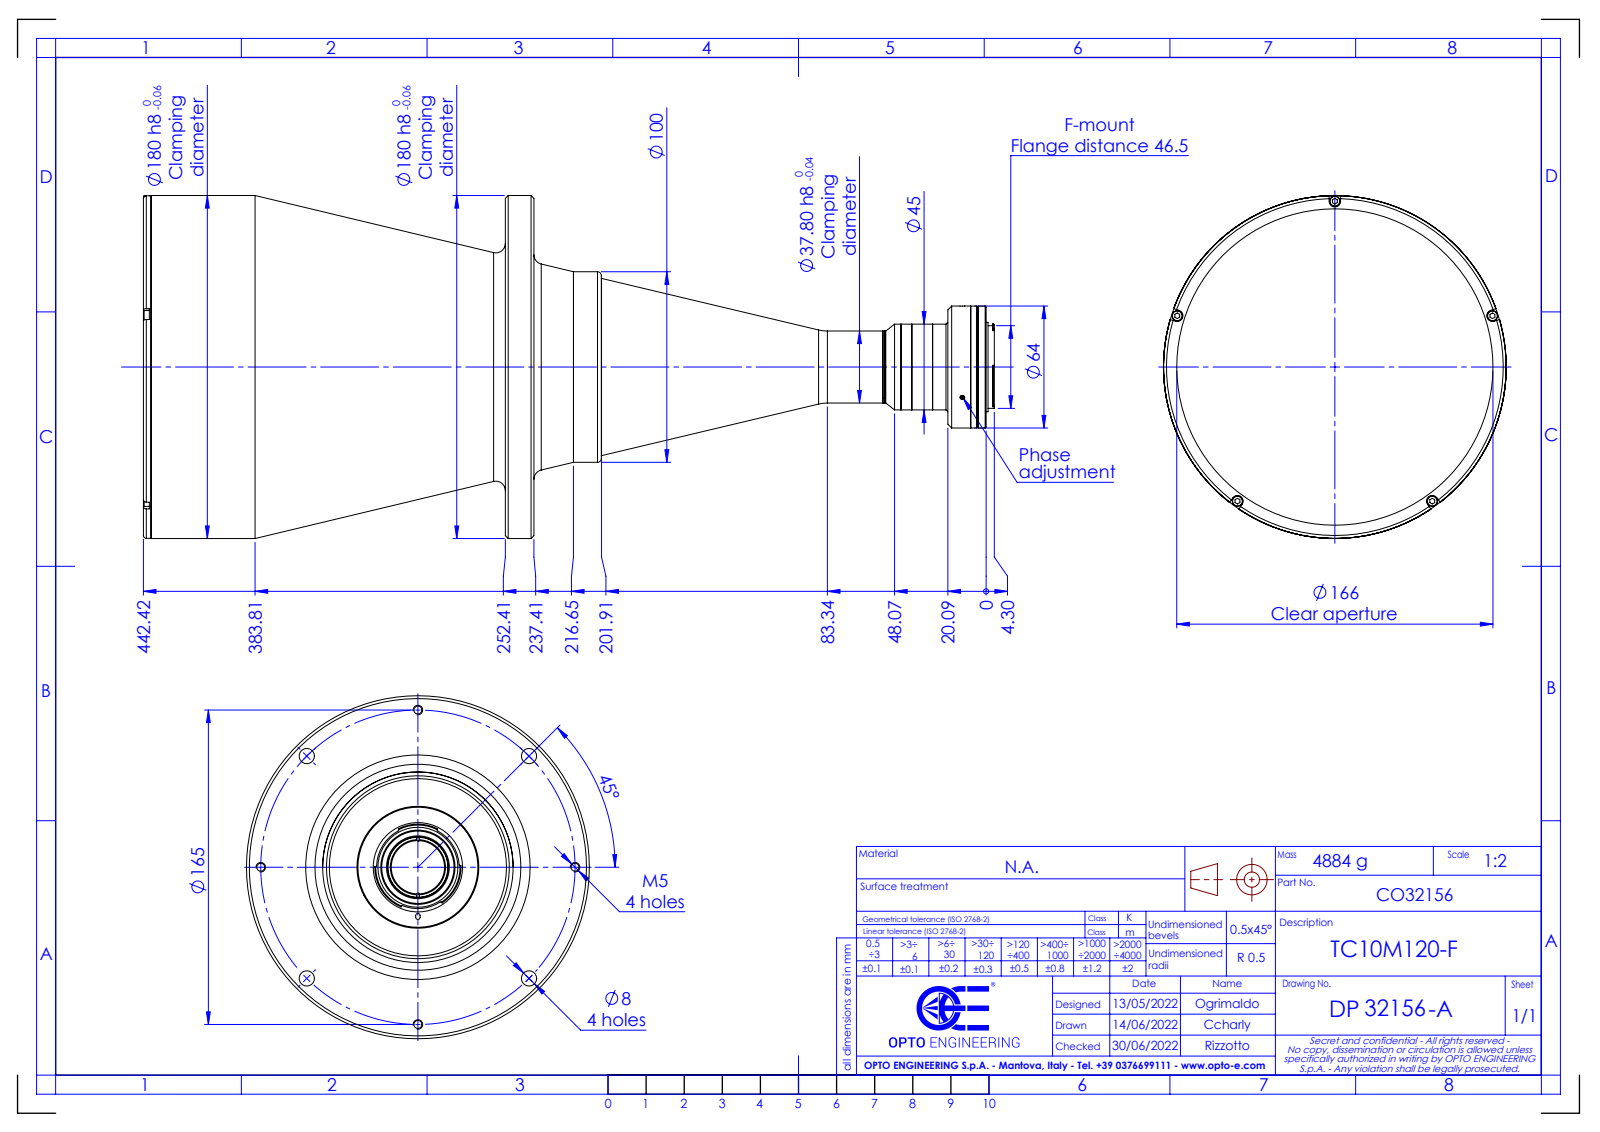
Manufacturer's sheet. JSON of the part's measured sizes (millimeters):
{"part_name": "DP32156-A_TC10M120-F", "step_written_by": "SolidWorks 2021 (CONFIG_CONTROL_DESIGN)", "units": "millimeters", "bodies": {"solids": 0, "faces": 193, "planar": 55, "cylindrical": 89, "other": 49}, "overall_size": [446.72, 180, 180], "round_holes": [[4.2, 4], [8, 4], [2.5, 3], [33, 1], [42, 1], [166, 1], [170.8, 1]], "round_bosses_or_shafts": [[5.5, 5], [180, 1], [179.8, 1], [100, 1], [93, 1], [64, 1], [63.5, 1], [46.9, 1]], "partial_cylinders_radius": [[3, 3], [0.5, 2], [1.15, 1], [22.65, 1]], "face_to_face_distances": [15, 4, 190.01, 205.01, 186.01, 201.01, 438.41, 423.82, 419.82, 233.81], "hole_center_spacings": [63.14, 152.44, 82.5, 82.51, 116.67, 116.68, 165, 165.01]}
